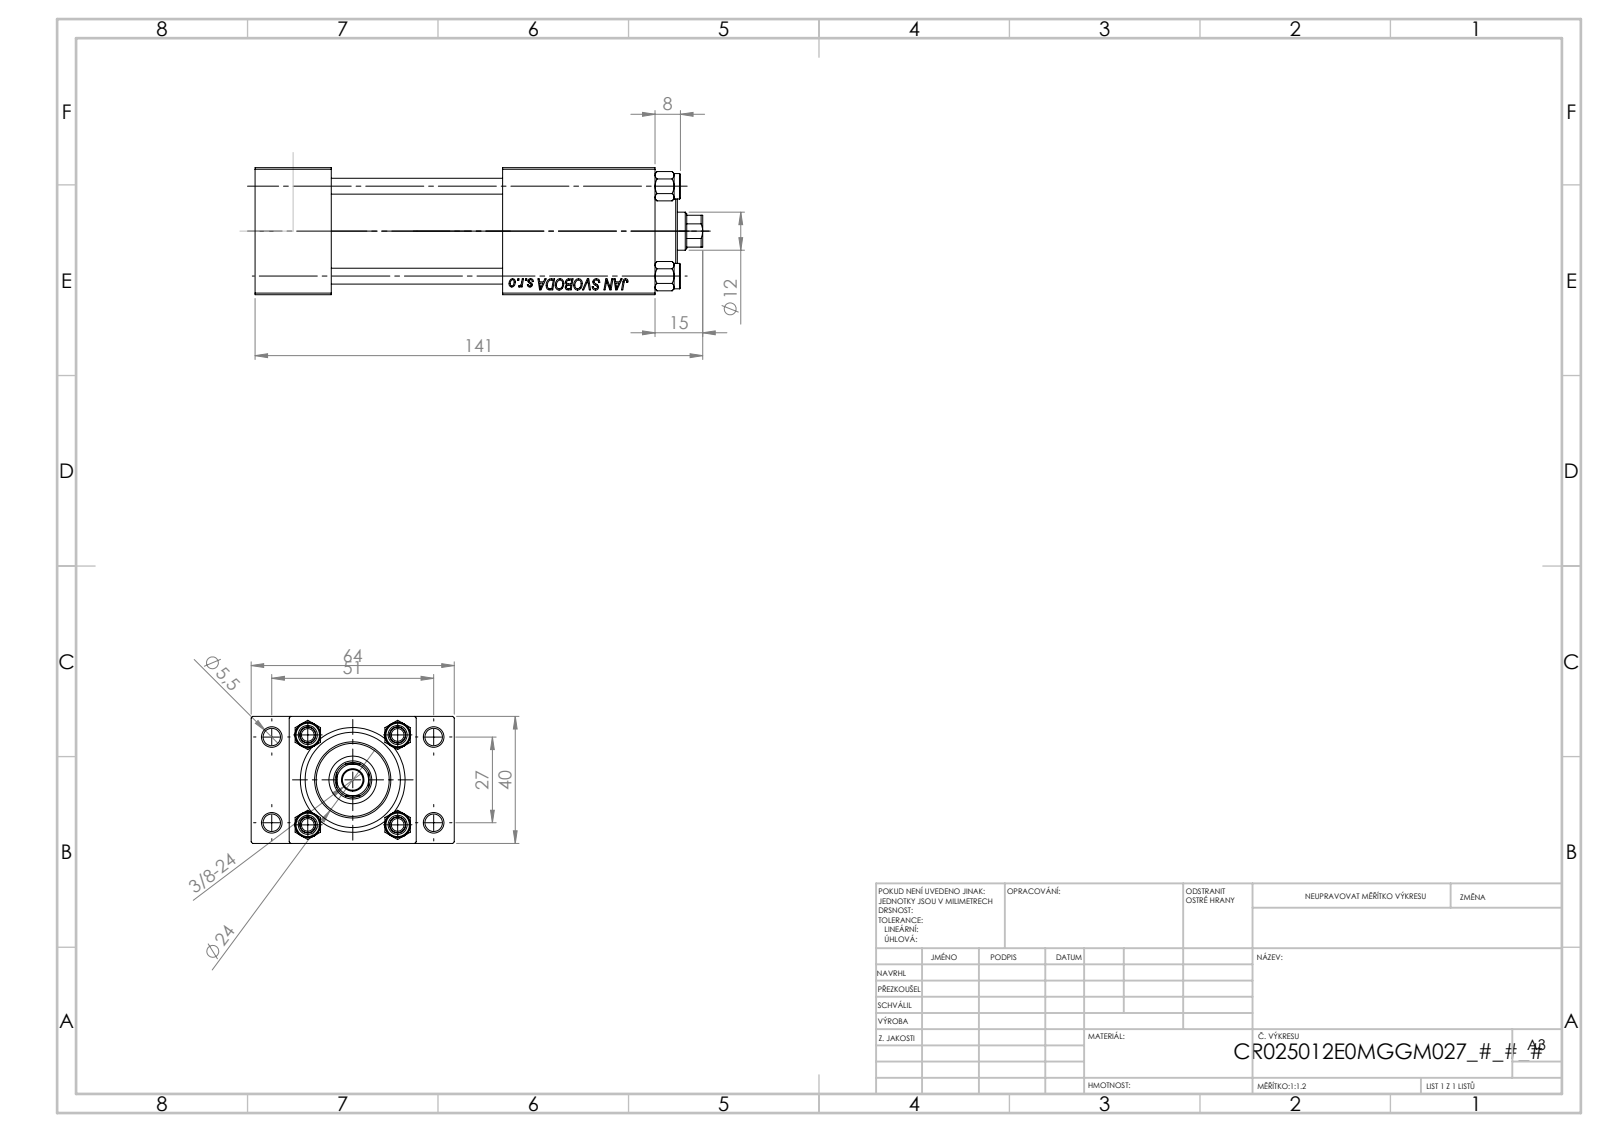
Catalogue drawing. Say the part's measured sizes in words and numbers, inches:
The part is named "NUT_M5_E; V215CR_TYCINKA_E; V215CR_VCP_E; V215_VC_A (+1 more)". Its 3-D file was written by "SolidWorks 2019 (CONFIG_CONTROL_DESIGN)". It is 11 solids with 1136 faces: 497 planar, 87 cylindrical and 552 other. Overall it measures 5.551 by 2.52 by 1.575 inches. Its volume is 10.2 cubic inches and its surface area 99.26 square inches. Round holes: 4 of diameter 0.197, 4 of diameter 0.217, 3 of diameter 0.787, 2 of diameter 0.276, 2 of diameter 0.518, 1 of diameter 0.256, 1 of diameter 0.472, 1 of diameter 0.591, 1 of diameter 0.984, 1 of diameter 1.181. Round bosses or shafts: 4 of diameter 0.315, 1 of diameter 1.22, 1 of diameter 0.945. Partial cylindrical surfaces (rounded edges, fillets, slot ends): 1 of radius 0.217. The main face-to-face distances are 1.575, 0.945, 0.472, 2.047, 4.961, 4.016, 3.831, 2.886, 1.13, 2.52. The hole center spacings are 0.448, 0.788, 1.114, 1.136, 1.177, 1.561, 1.903, 1.063.
